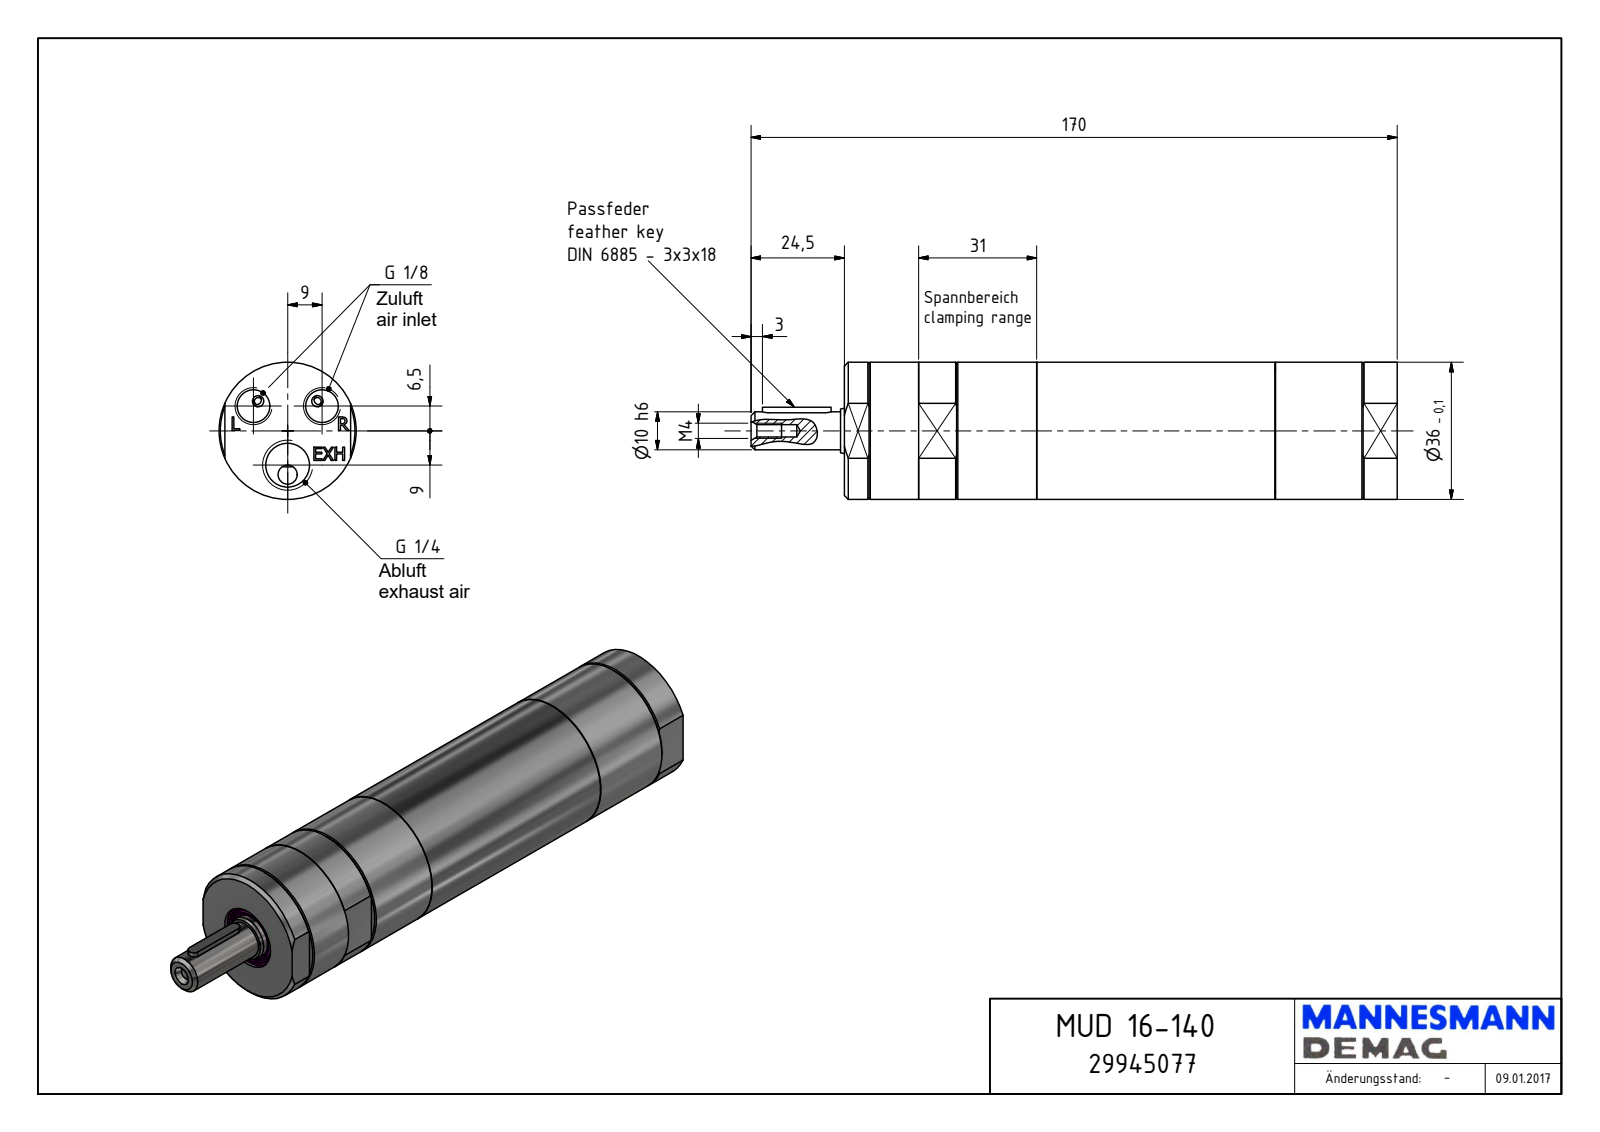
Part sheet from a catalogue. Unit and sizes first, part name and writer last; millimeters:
Units: millimetres
Overall size (bounding box): 169.7 × 36 × 36
Round holes (diameter × count): ⌀8.57 ×2, ⌀3.24 ×1, ⌀11.45 ×1, ⌀15.5 ×1, ⌀17 ×1, ⌀32.38 ×1
Round bosses / shafts (diameter × count): ⌀36 ×1, ⌀32.19 ×1, ⌀32 ×1, ⌀11.95 ×1, ⌀10 ×1
Partial cylindrical surfaces — rounded edges, fillets, slot ends (radius × count): R1.5 ×2
Main face-to-face distances: 145.2, 33, 134.91, 10.29, 50.5, 84.41, 94.7, 50.55, 84.36, 94.65
Hole centre spacings: 11.1, 17.92, 9, 18
Volume: 146 392 mm³ · Surface area: 21 688 mm²
Bodies: 1 solid, 142 faces (90 planar, 23 cylindrical, 29 other)
Part name (STEP PRODUCT): MUD 16-140_29945077
STEP written by: Autodesk Inventor 2018 (AUTOMOTIVE_DESIGN)
